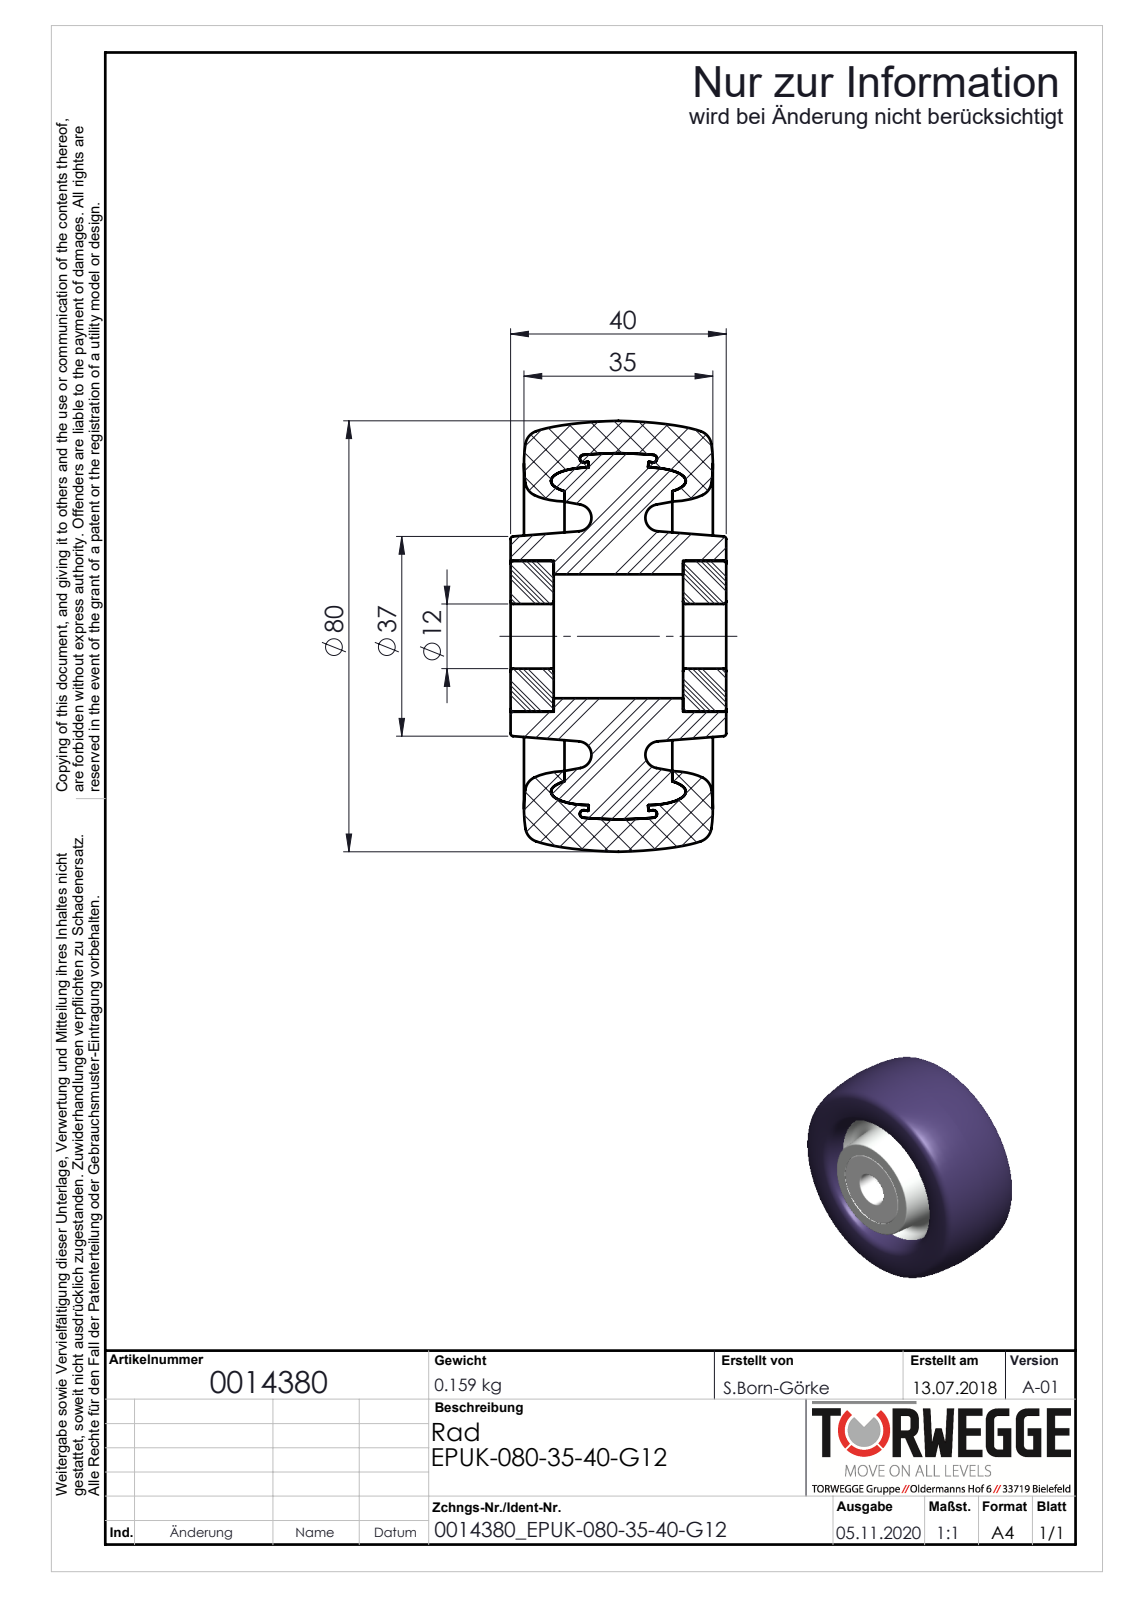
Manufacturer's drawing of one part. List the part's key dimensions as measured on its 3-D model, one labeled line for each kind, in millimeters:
Part name (STEP PRODUCT): 0014380
STEP written by: SolidWorks 2020 (AUTOMOTIVE_DESIGN)
Units: millimetres
Bodies: 3 solids, 179 faces (22 planar, 21 cylindrical, 136 other)
Overall size (bounding box): 80 × 80 × 40
Volume: 139 496 mm³ · Surface area: 30 689 mm²
Round holes (diameter × count): ⌀12 ×1, ⌀23 ×1, ⌀28 ×1
Partial cylindrical surfaces — rounded edges, fillets, slot ends (radius × count): R31.4 ×1
Main face-to-face distances: 8, 32, 40, 24, 10, 30, 2, 22, 20
